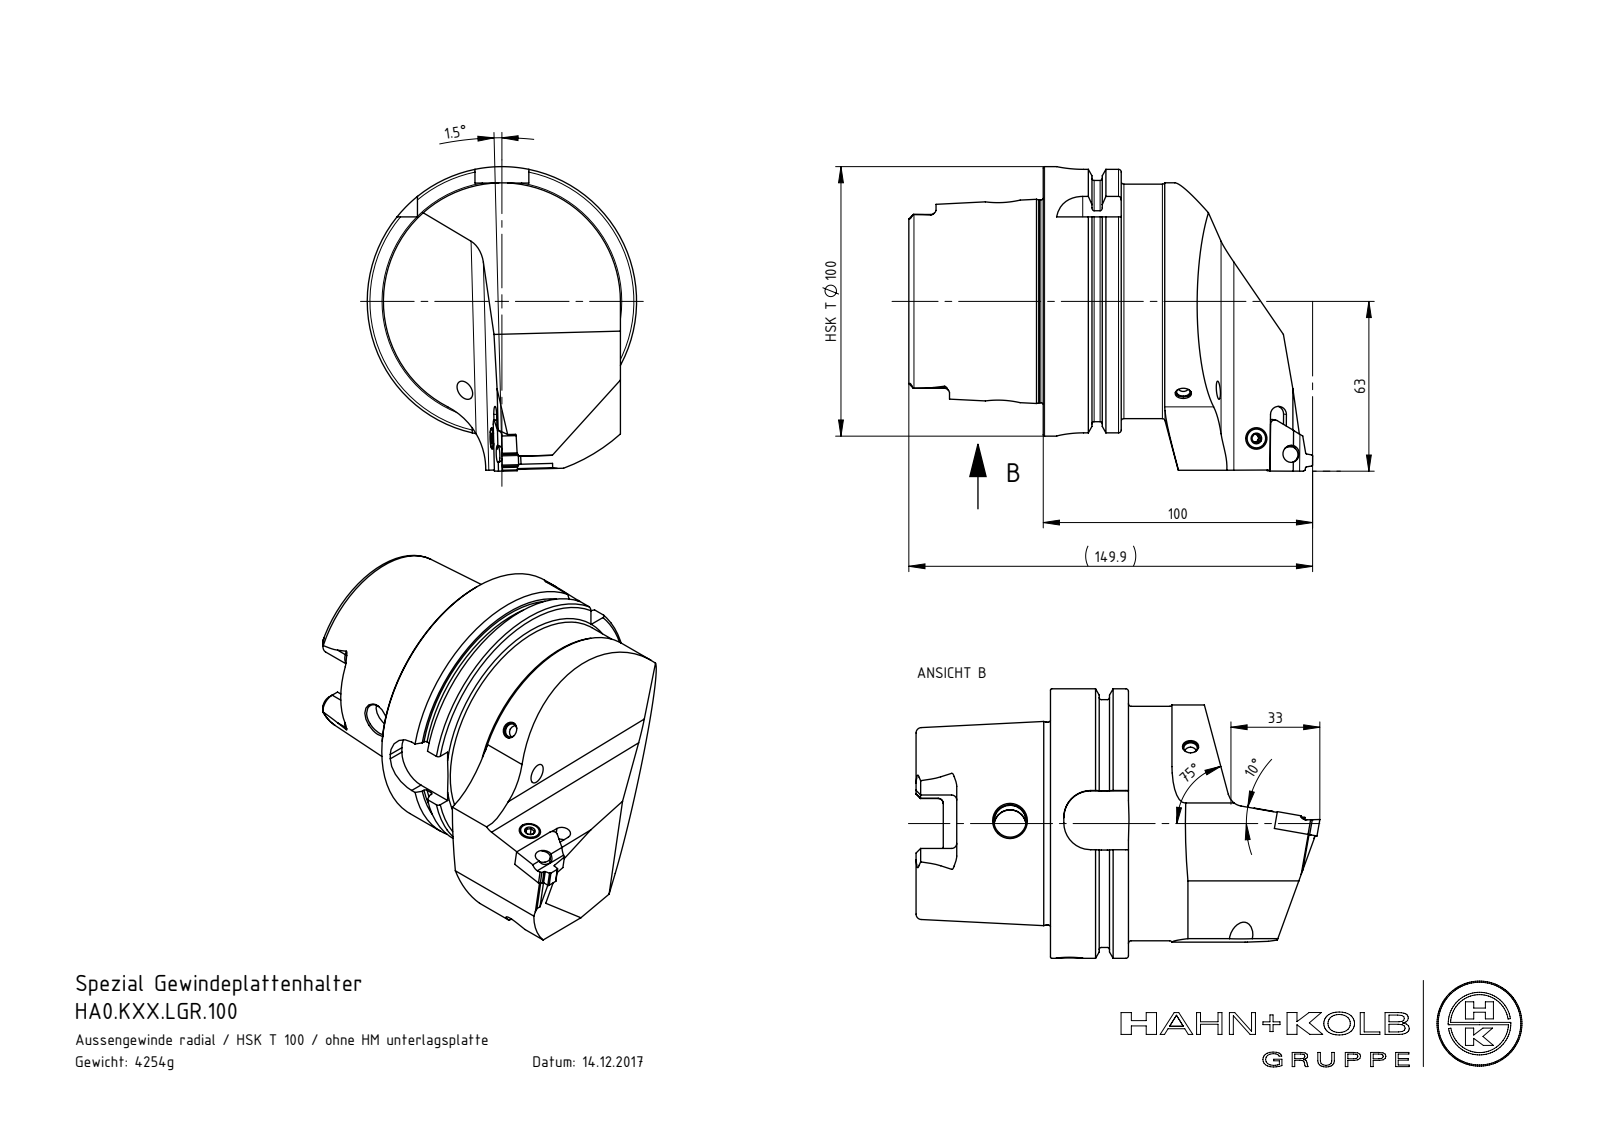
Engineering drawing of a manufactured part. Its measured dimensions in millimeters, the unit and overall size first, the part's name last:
Units: millimetres
Overall size (bounding box): 149.91 × 113 × 100
Round holes (diameter × count): ⌀5 ×2, ⌀12 ×2, ⌀6.35 ×1, ⌀7 ×1, ⌀8.4 ×1, ⌀10 ×1, ⌀22.5 ×1, ⌀26 ×1, ⌀53 ×1, ⌀63 ×1
Round bosses / shafts (diameter × count): ⌀6 ×2, ⌀100 ×1, ⌀91.95 ×1, ⌀87 ×1, ⌀75.26 ×1, ⌀8 ×1, ⌀7.9 ×1, ⌀6.4 ×1
Partial cylindrical surfaces — rounded edges, fillets, slot ends (radius × count): R1.9 ×6, R0.4 ×4, R4.88 ×4, R10 ×4, R3.5 ×3, R0.3 ×2, R1.6 ×1, R2.5 ×1
Main face-to-face distances: 12.45, 28.95, 16.5, 49.9, 62.35, 78.85, 87.8, 78.2, 28.3, 15.85
Hole centre spacings: 14.38
Volume: 542 993 mm³ · Surface area: 71 362 mm²
Bodies: 6 solids, 327 faces (103 planar, 99 cylindrical, 125 other)
Part name (STEP PRODUCT): WCE-ER4.101.020_A; HA0.KXX.LGR.100; WCE-ER3.101.000_A; XNMT440612_TCMT16T308 (+2 more)
STEP written by: SolidWorks 2017 (AUTOMOTIVE_DESIGN)
